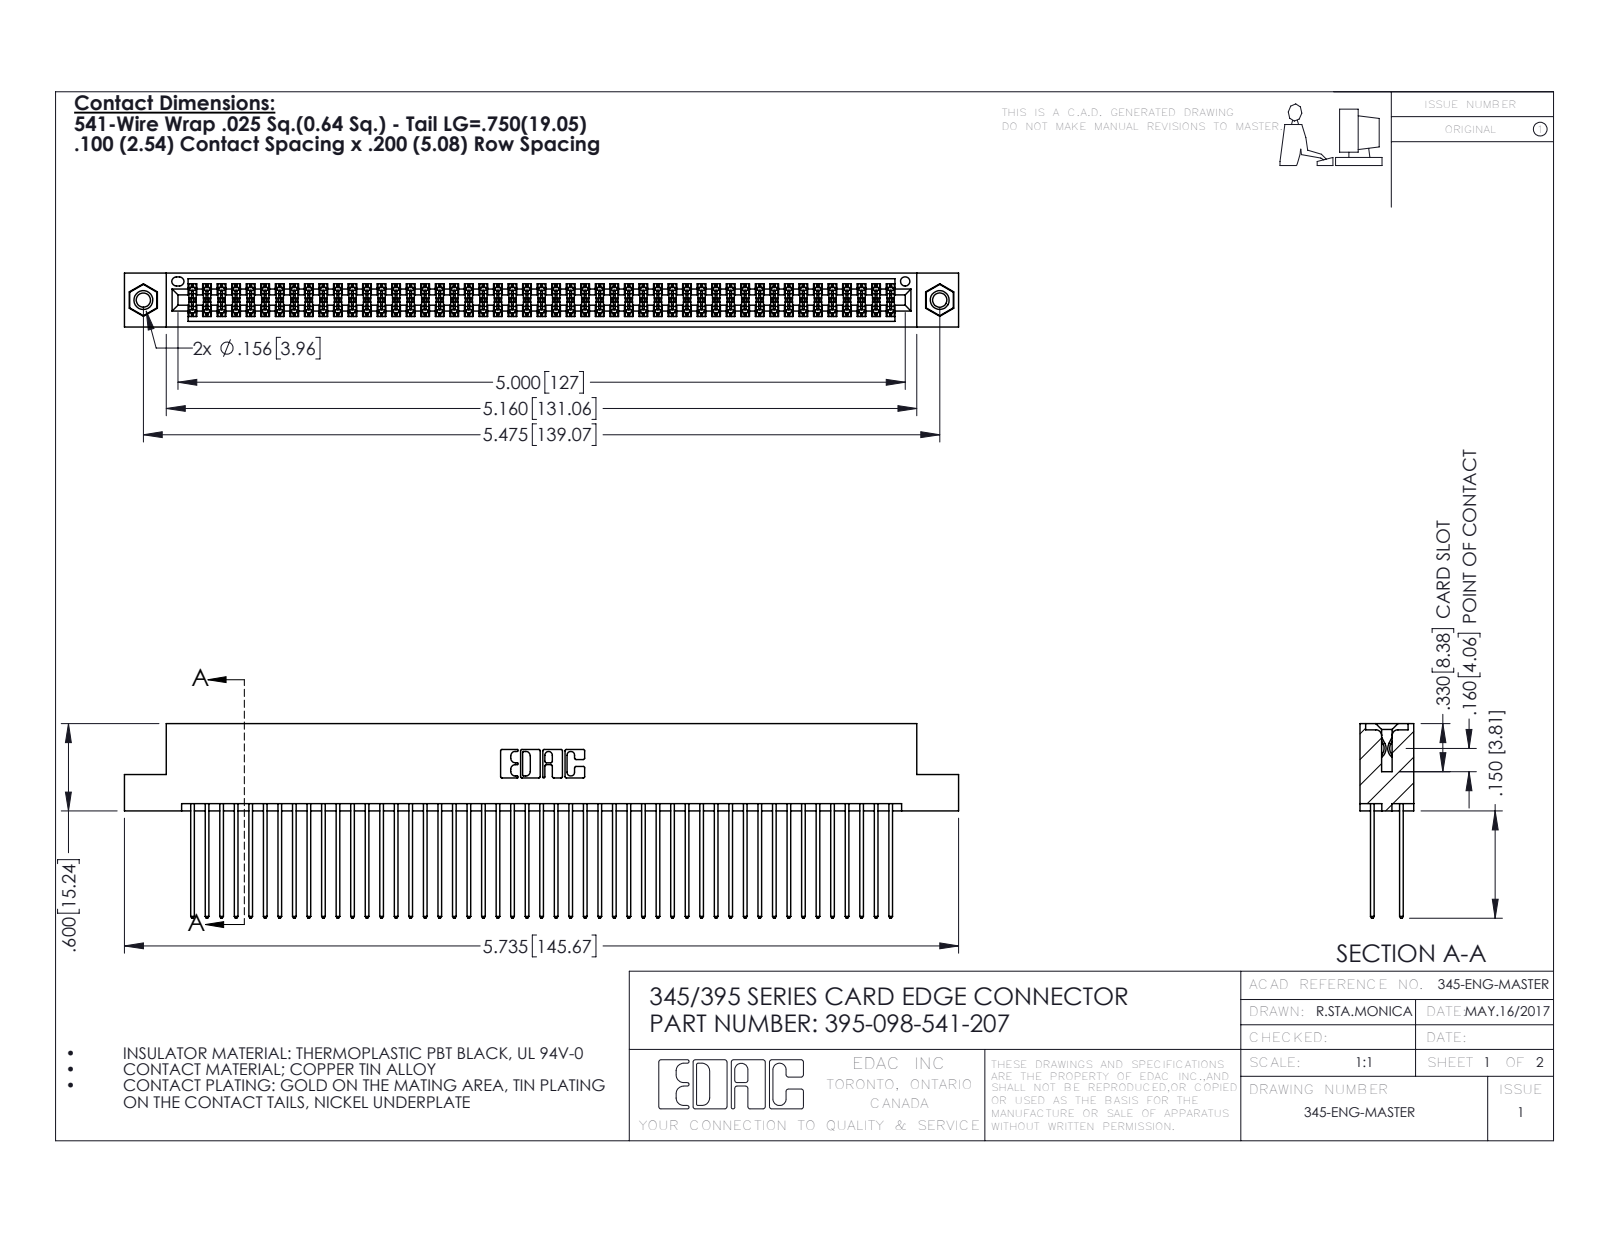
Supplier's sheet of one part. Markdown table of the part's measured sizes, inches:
| quantity | value |
| --- | --- |
| part name | 395-098-541-207; 345 Part_Flush Mounting Lugs - 0.156 Dia-TI; 345-250-001_345-250-005-103; 345-292-001_345-293-141 |
| STEP written by | SolidWorks 2016 (CONFIG_CONTROL_DESIGN) |
| units | inches |
| bodies | 101 solids, 5086 faces (3346 planar, 1724 cylindrical, 16 other) |
| overall size | 5.735 × 1.337 × 0.37 |
| volume | 0.901 in³ |
| surface area | 38.18 in² |
| round holes (diameter × count) | 0.098 × 2, 0.125 × 2, 0.156 × 2, 0.064 × 1 |
| round bosses / shafts (diameter × count) | 0.155 × 2 |
| partial cylindrical surfaces (radius × count) | 0.006 × 147, 0.01 × 98, 0.01 × 22, 0.007 × 6, 0.031 × 6, 0.026 × 3, 0.014 × 2, 0.019 × 2 |
| main face-to-face distances | 0.072, 0.298, 0.2, 0.098, 0.272, 0.025, 0.225, 0.37, 0.175, 0.149 |
| hole center spacings | 0.27, 5.239, 5.475 |
